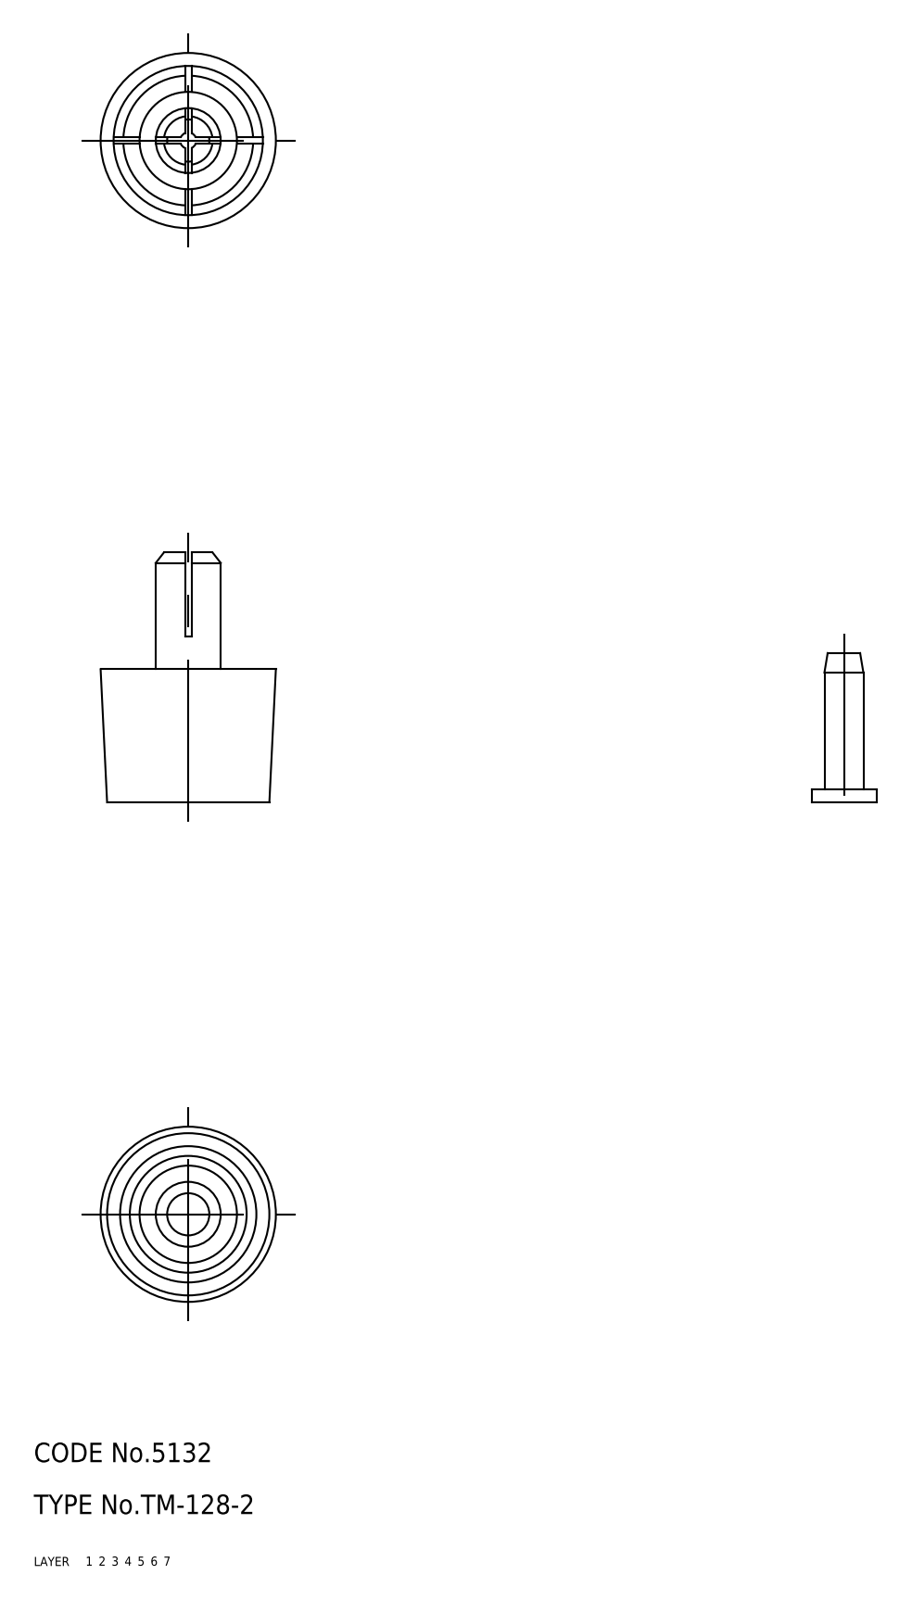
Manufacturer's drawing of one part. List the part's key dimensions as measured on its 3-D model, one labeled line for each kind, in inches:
Part name (STEP PRODUCT): pin; foot; TM_128_2_15250_36
STEP written by: CADfix (AUTOMOTIVE_DESIGN)
Units: inches
Bodies: 2 solids, 82 faces (0 planar, 0 cylindrical, 82 other)
Overall size (bounding box): 1.516 × 1.063 × 1.063
Volume: 0.466 in³ · Surface area: 11.32 in²
